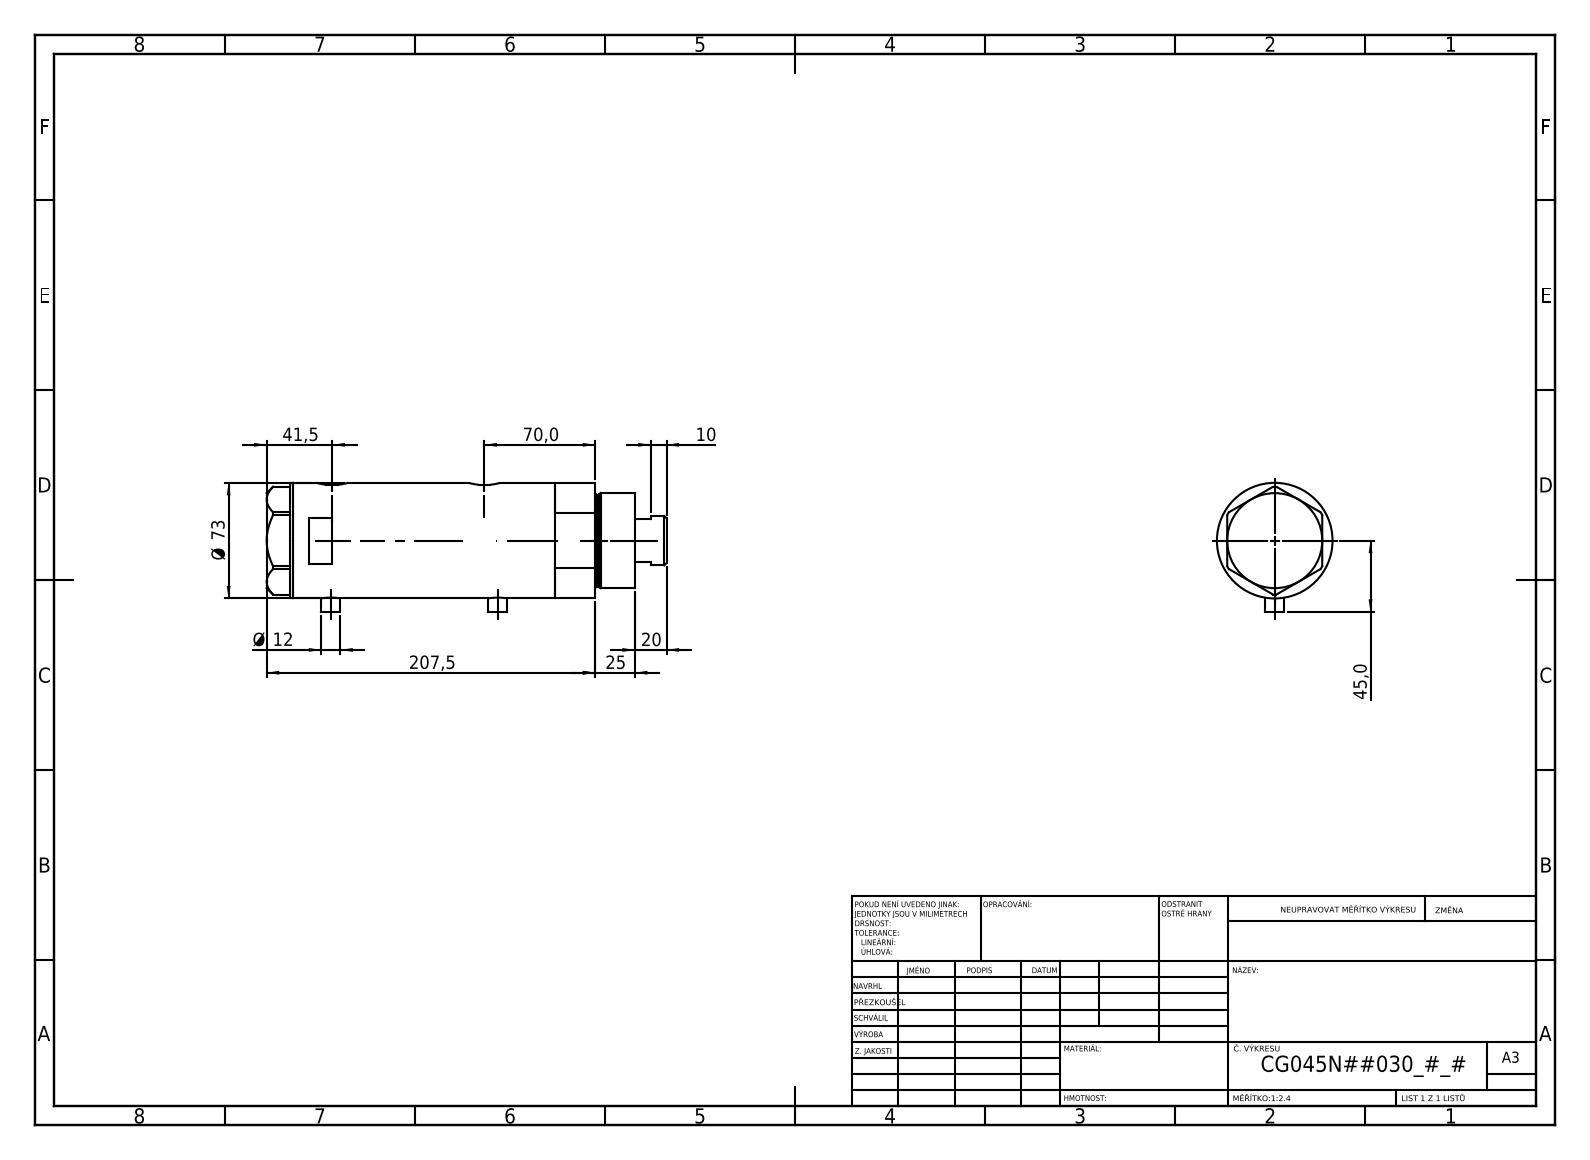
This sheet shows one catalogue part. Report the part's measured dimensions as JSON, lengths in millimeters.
{"part_name": "V270CG_VC; V270CG_FRONT; V270CG_BACK; V270CG_MIDDLE", "step_written_by": "SolidWorks 2019 (CONFIG_CONTROL_DESIGN)", "units": "millimeters", "bodies": {"solids": 4, "faces": 120, "planar": 49, "cylindrical": 51, "other": 20}, "overall_size": [252.5, 81.5, 73], "volume_mm3": 901868, "surface_area_mm2": 149768, "round_holes": [[12.5, 2], [13.16, 2], [10.5, 1], [32, 1], [33.5, 1], [45, 1], [48, 1], [64, 1]], "round_bosses_or_shafts": [[12, 2], [73, 1], [60, 1], [58, 1], [31, 1]], "partial_cylinders_radius": [[10, 2]], "face_to_face_distances": [95, 121, 26, 16.5, 42.5, 137.5, 2, 216, 232.5, 190], "hole_center_spacings": [1, 8.5, 96, 97, 104.5, 105.5]}
